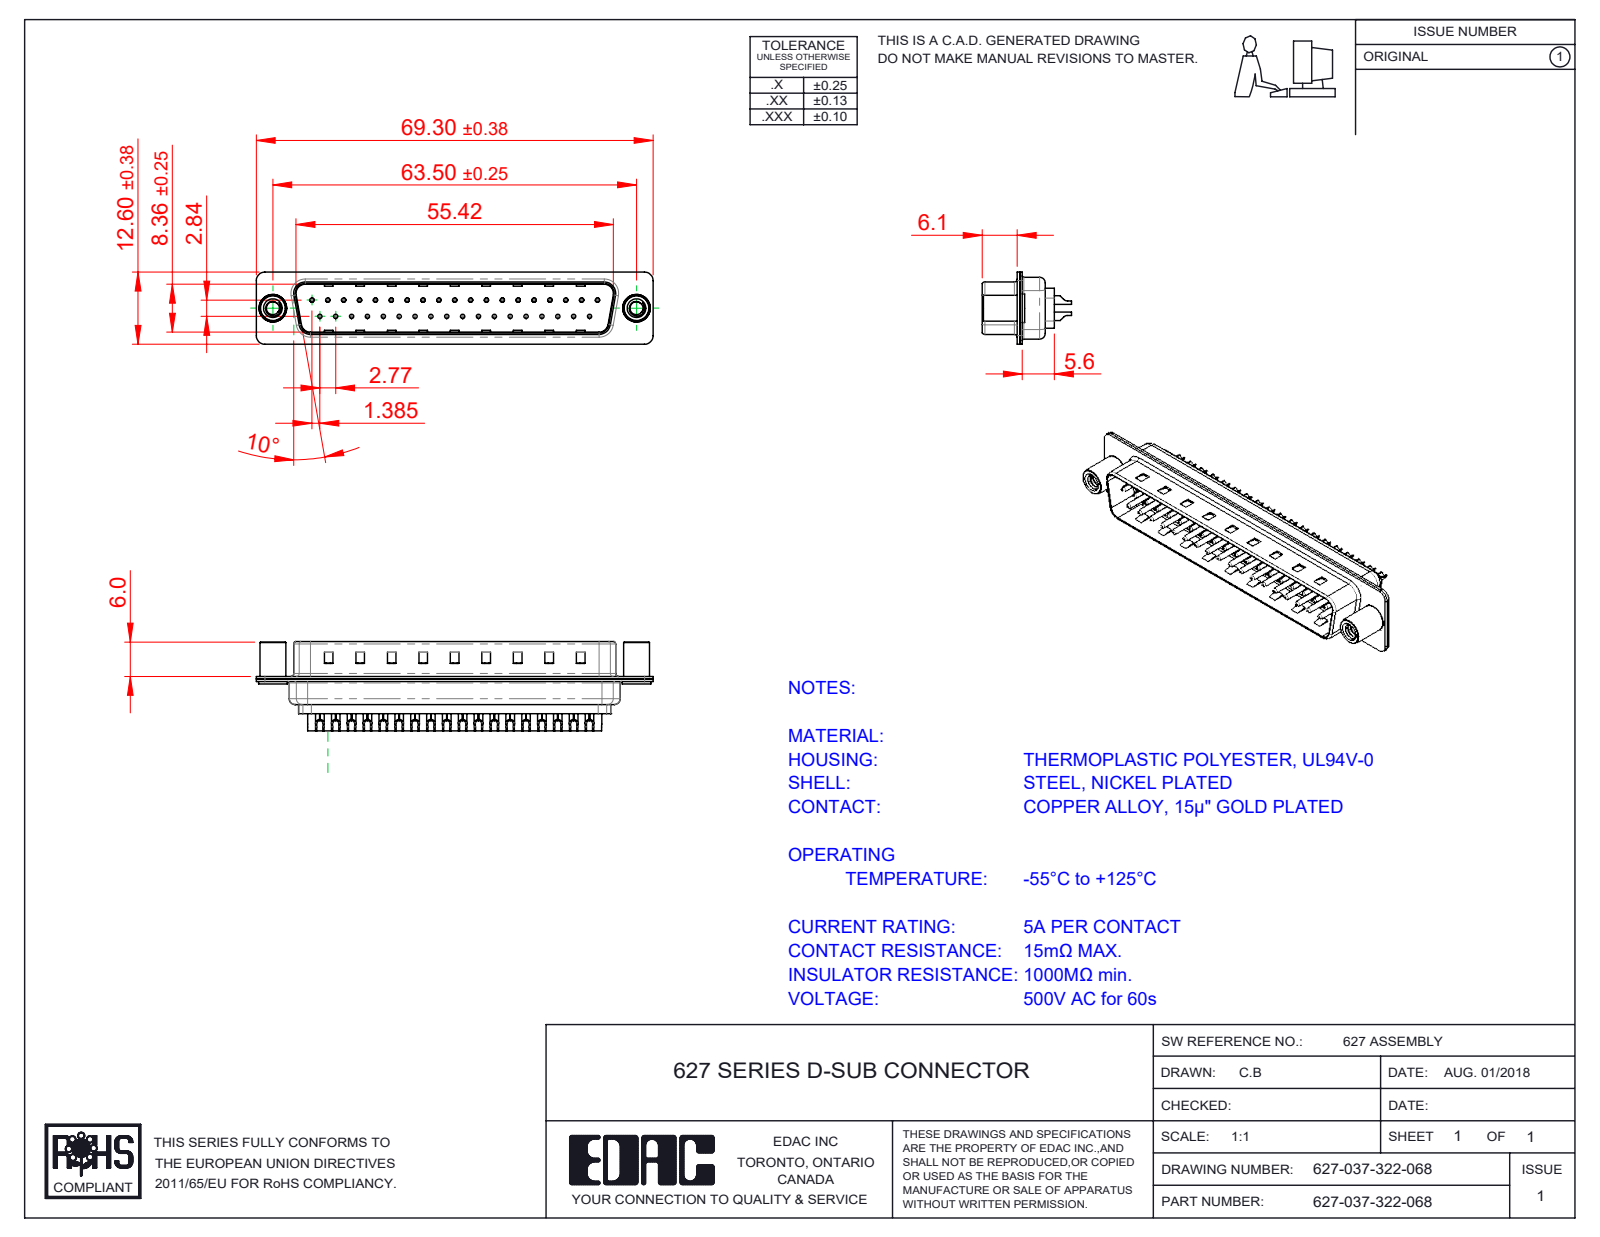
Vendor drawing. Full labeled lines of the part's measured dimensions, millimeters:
Part name (STEP PRODUCT): 627-037-322-068; 627 Housing_37 LP; 627 Shell Rear_37 Contacts; 627 Contact Row 2_22L (+3 more)
STEP written by: SolidWorks 2020 (CONFIG_CONTROL_DESIGN)
Units: millimetres
Bodies: 42 solids, 2814 faces (723 planar, 1242 cylindrical, 849 other)
Overall size (bounding box): 69.3 × 15.35 × 12.6
Volume: 3 778 mm³ · Surface area: 10 952 mm²
Round holes (diameter × count): ⌀0.35 ×37, ⌀1.1 ×37, ⌀1.6 ×37, ⌀2.26 ×2, ⌀4 ×2, ⌀4.8 ×2
Round bosses / shafts (diameter × count): ⌀2 ×37, ⌀1.5 ×37, ⌀0.75 ×37, ⌀5 ×2, ⌀4.9 ×2, ⌀4.5 ×2
Partial cylindrical surfaces — rounded edges, fillets, slot ends (radius × count): R1.5 ×16, R2 ×12, R0.5 ×8, R1.6 ×8, R1 ×6, R0.25 ×4, R0.6 ×4, R0.65 ×4
Main face-to-face distances: 0.4, 0.82, 9.58, 0.45, 8.76, 1.5, 0.9, 1.4, 6.05, 0.42
Hole centre spacings: 3.16, 2.77, 5.54, 8.31, 5.04, 10.1, 11.08, 12.78
